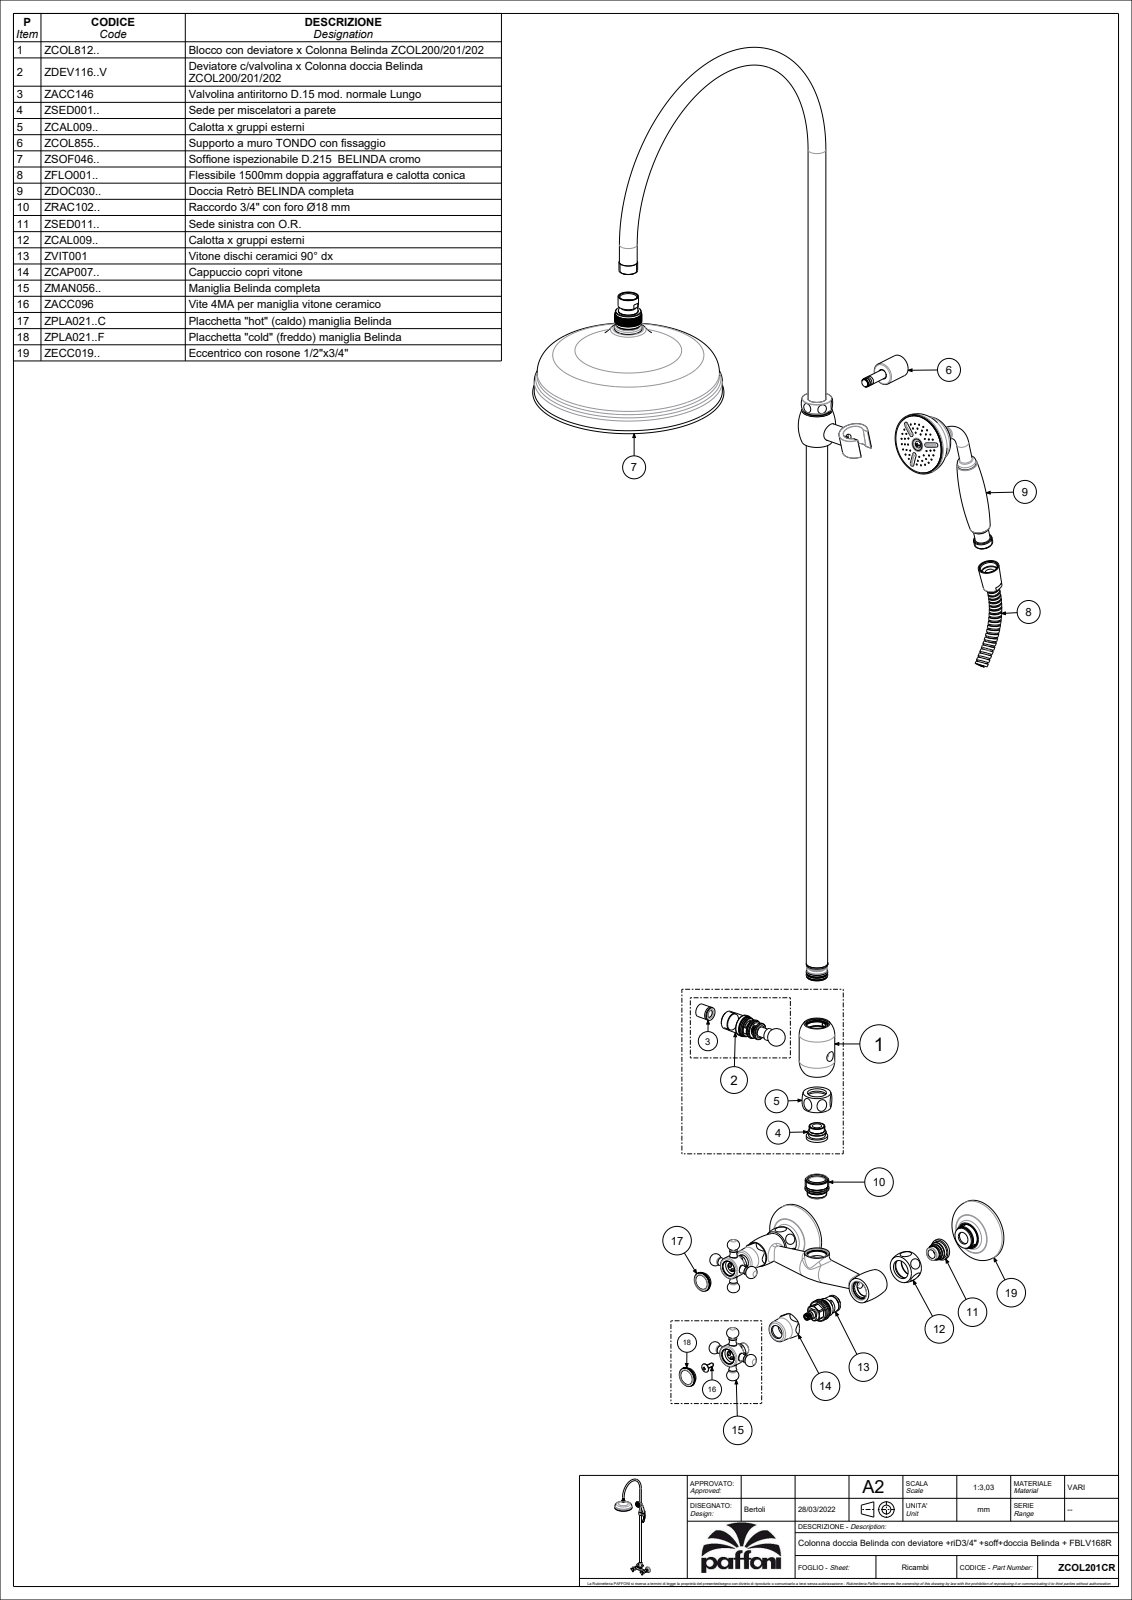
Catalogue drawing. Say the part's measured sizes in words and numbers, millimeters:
The part is named "ZCOL201CR". Its 3-D file was written by "CREO PARAMETRIC BY PTC INC, 2021404 (CONFIG_CONTROL_DESIGN)". It is 9 solids with 3710 faces: 1557 planar, 1150 cylindrical and 1003 other. Overall it measures 1317.9 by 512 by 220 millimeters. Its volume is 1 873 000 cubic millimeters and its surface area 512 697 square millimeters. Round holes: 100 of diameter 2, 45 of diameter 1.2, 5 of diameter 5, 4 of diameter 17, 4 of diameter 25, 3 of diameter 10.2, 3 of diameter 13, 3 of diameter 16.5, 3 of diameter 21.5, 3 of diameter 24.1, 3 of diameter 27.5, 2 of diameter 3. Round bosses or shafts: 4 of diameter 24, 4 of diameter 21, 4 of diameter 20.5, 4 of diameter 14, 3 of diameter 9, 3 of diameter 7, 2 of diameter 70, 2 of diameter 28.14. Partial cylindrical surfaces (rounded edges, fillets, slot ends): 34 of radius 0.1, 18 of radius 0.5, 6 of radius 0.3, 4 of radius 1, 2 of radius 5.25, 2 of radius 9.4, 2 of radius 11, 1 of radius 6.75. The main face-to-face distances are 15, 32, 2, 27.5, 17.5, 0.5, 18.5, 11, 11.5, 6.5. The hole center spacings are 24, 23.99, 18.99, 14, 19, 14.01, 57, 11.08.
